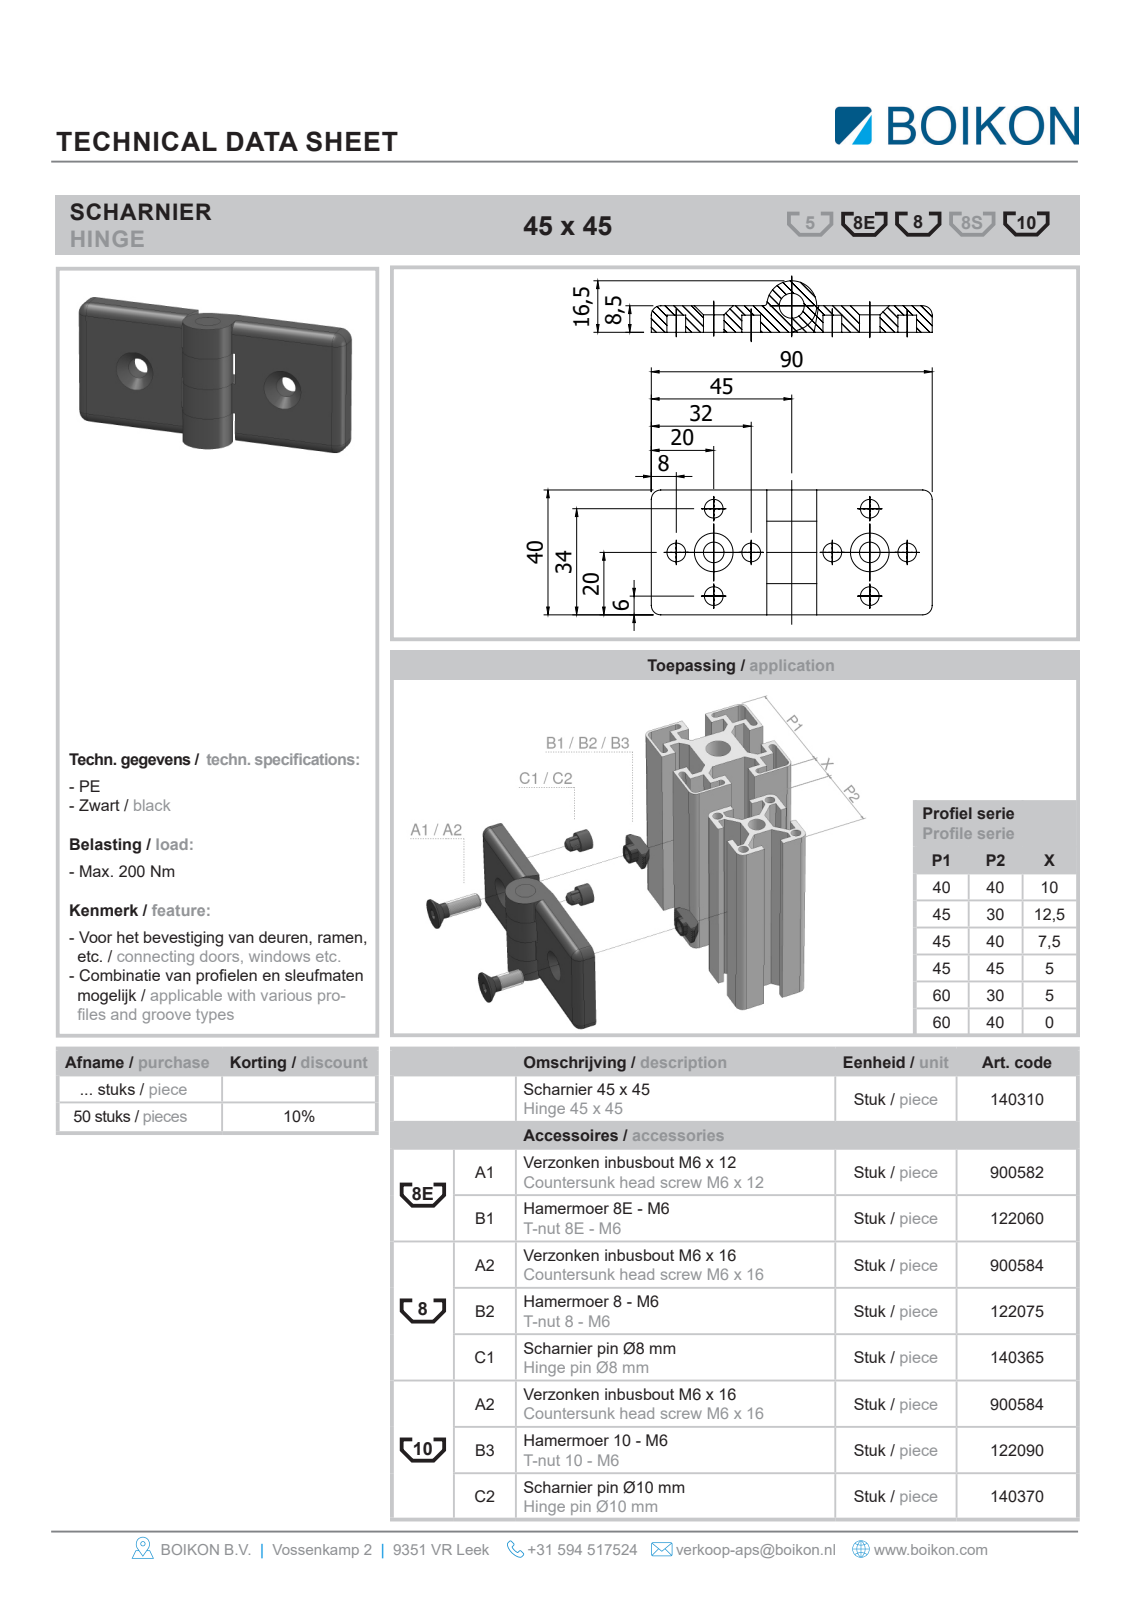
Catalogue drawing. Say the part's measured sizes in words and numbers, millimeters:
The part is named "Root; 140310Scharnier 45x45 8 en 10BOIKON". Its 3-D file was written by "HiCAD 2013 1802.4 Build 509 (AUTOMOTIVE_DESIGN)". It is 3 solids with 75 faces: 40 planar, 29 cylindrical and 6 other. Overall it measures 90 by 40 by 17 millimeters. Its volume is 31 324 cubic millimeters and its surface area 14 128 square millimeters. Round holes: 8 of diameter 6, 2 of diameter 6.5, 1 of diameter 8. Round bosses or shafts: 1 of diameter 16. Partial cylindrical surfaces (rounded edges, fillets, slot ends): 8 of radius 3.5. The main face-to-face distances are 8.5, 10, 20, 30, 40, 5.5, 3, 90, 37, 53. The hole center spacings are 18.44, 50, 12, 14, 40.5, 51.92, 63.56, 24.
